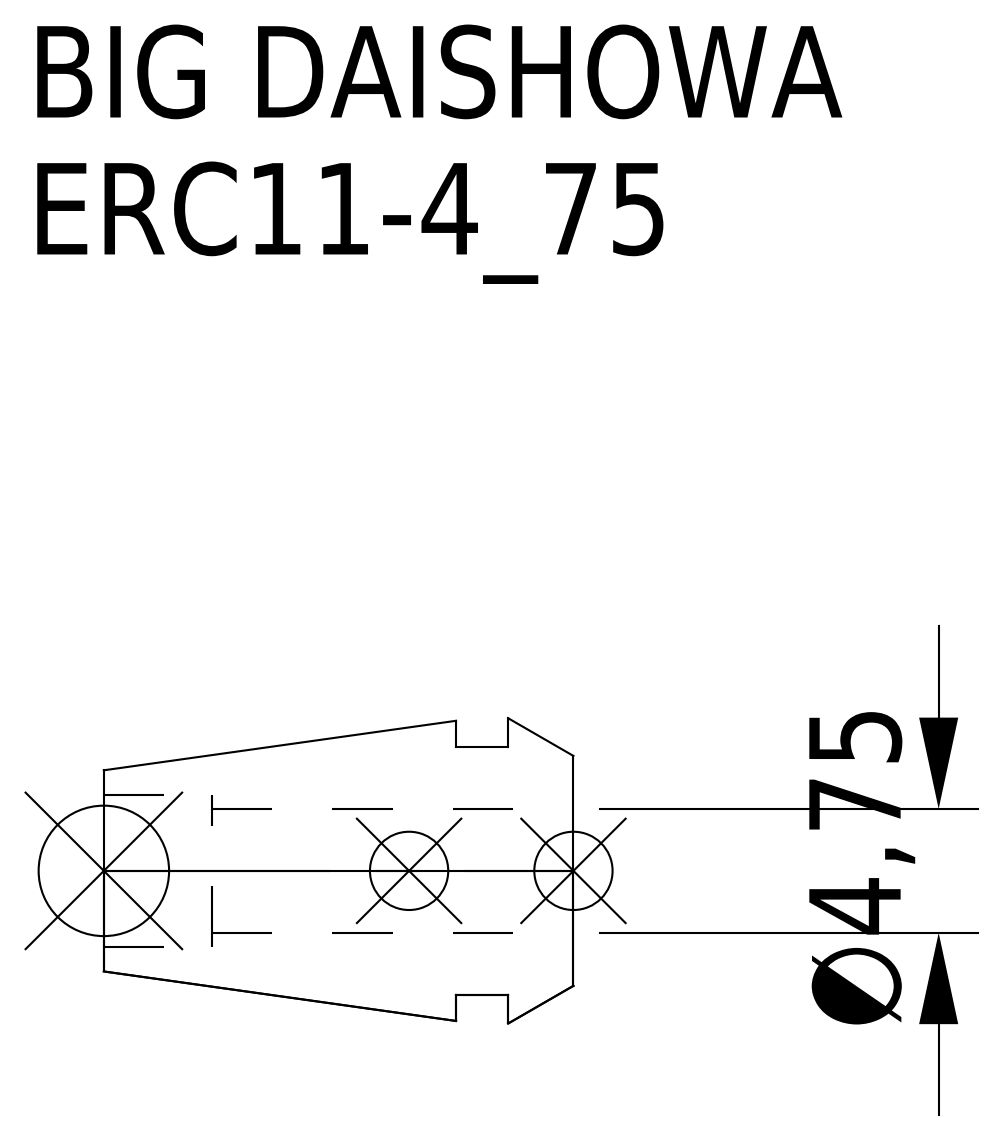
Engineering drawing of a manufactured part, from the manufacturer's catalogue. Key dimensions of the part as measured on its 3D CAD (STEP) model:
Part name (STEP PRODUCT): ERC11-4_75
STEP written by: CREO PARAMETRIC BY PTC INC, 2016380 (AUTOMOTIVE_DESIGN)
Units: millimetres
Bodies: 1 solid, 15 faces (5 planar, 6 cylindrical, 4 other)
Overall size (bounding box): 18 × 11.7 × 11.7
Volume: 986 mm³ · Surface area: 988 mm²
Round holes (diameter × count): ⌀4.75 ×1, ⌀5.8 ×1
Round bosses / shafts (diameter × count): ⌀9.5 ×1
Main face-to-face distances: 2.5, 4.5, 2, 18, 15.5, 13.5, 13.86, 11.36, 9.36, 4.14
